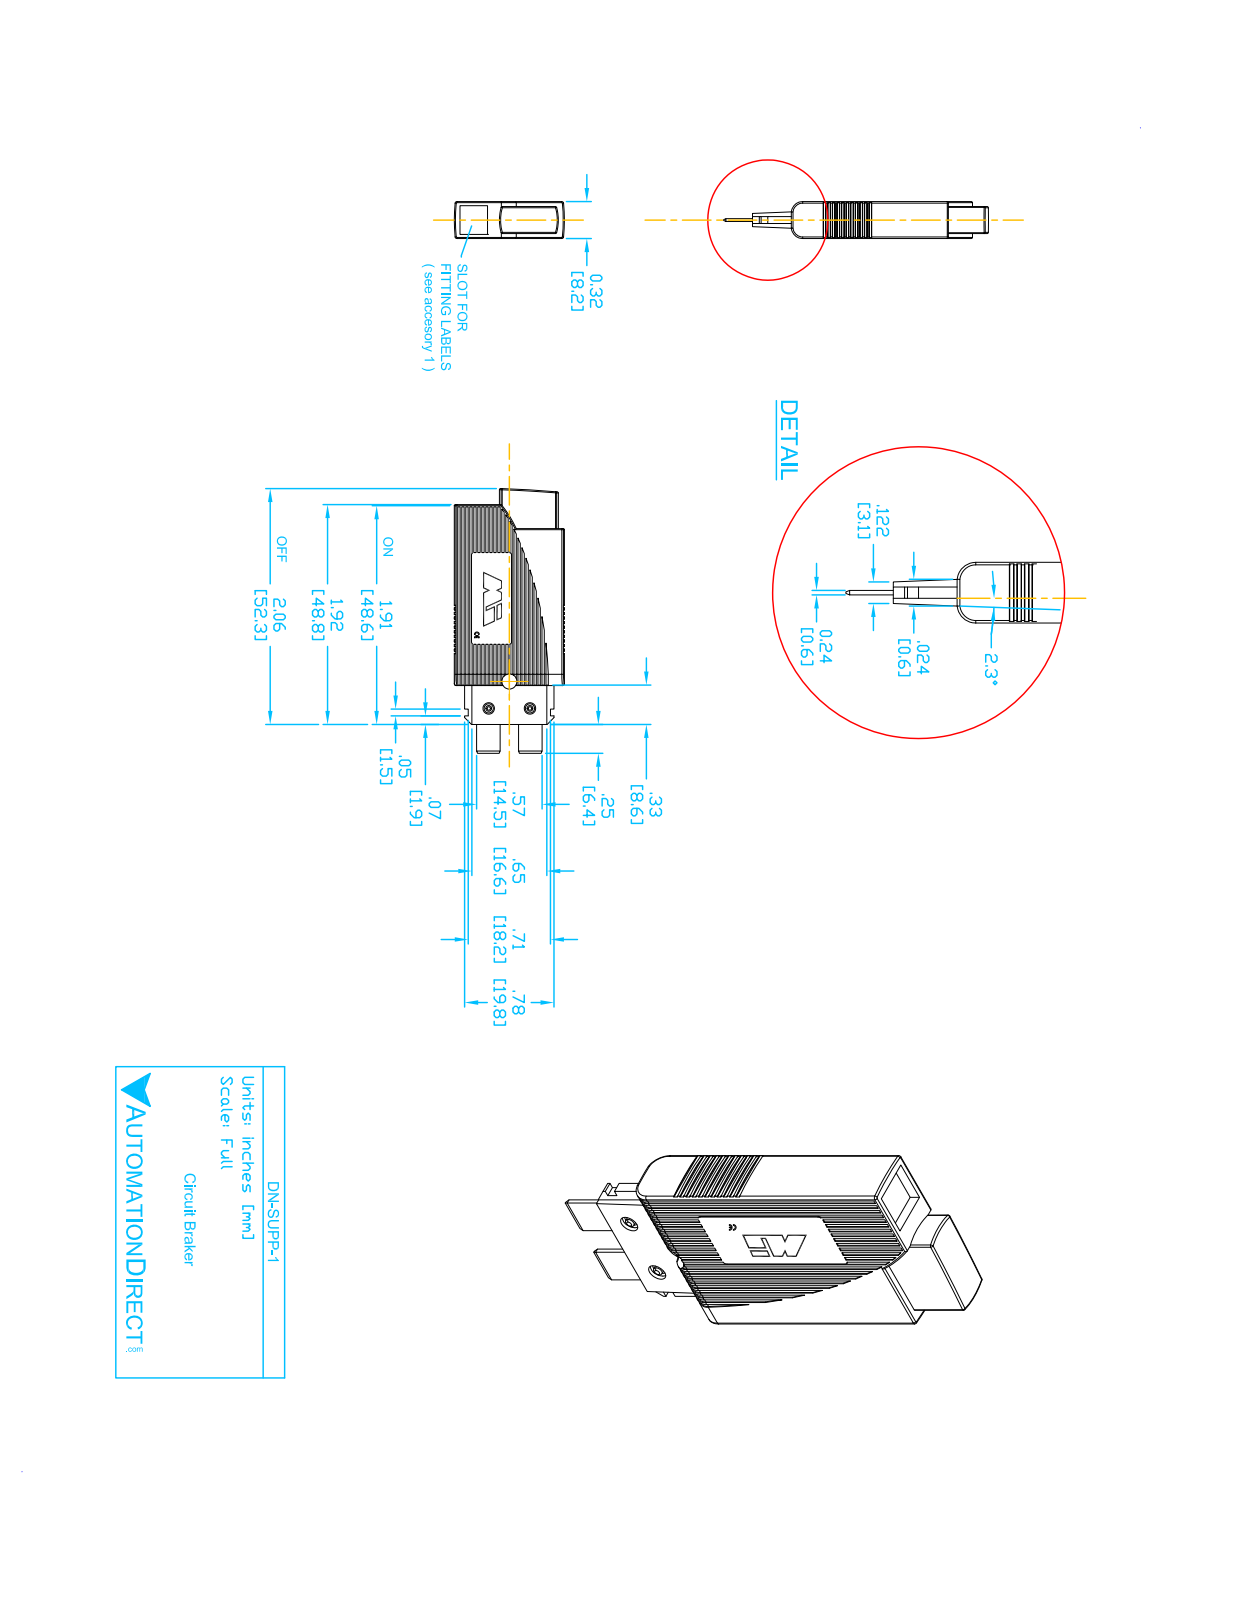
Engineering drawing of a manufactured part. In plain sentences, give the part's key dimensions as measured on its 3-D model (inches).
The part is named "DN-SUPP-1". Its 3-D file was written by "SolidWorks 2017 (AUTOMOTIVE_DESIGN)". It is 1 solid with 95 faces: 47 planar, 28 cylindrical and 20 other. Overall it measures 2.18 by 0.961 by 0.323 inches. Its volume is 0.505 cubic inches and its surface area 5.231 square inches. Partial cylindrical surfaces (rounded edges, fillets, slot ends): 21 of radius 0.012, 2 of radius 0.157, 1 of radius 2.165, 1 of radius 2.331, 1 of radius 2.362. The main face-to-face distances are 0.323, 0.961, 0.15, 0.173, 0.031, 0.291, 0.118, 0.142, 0.024, 0.14.
